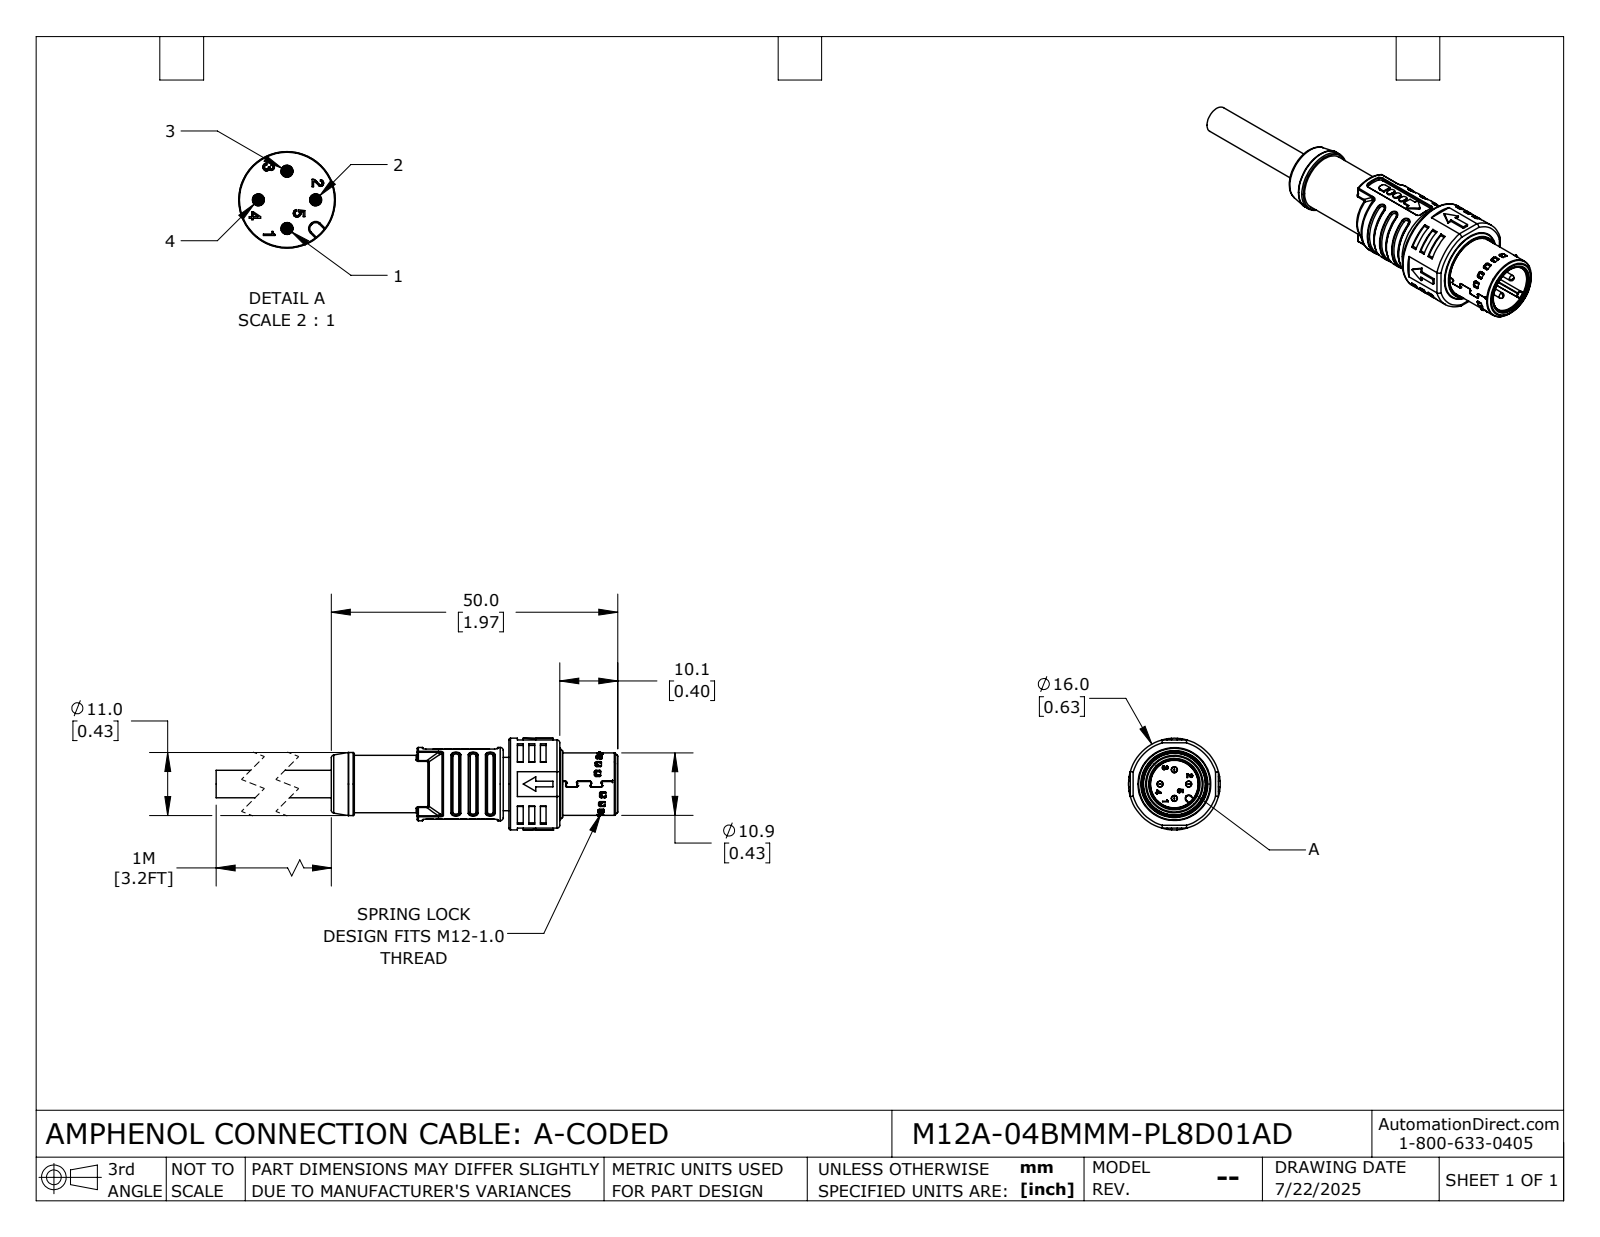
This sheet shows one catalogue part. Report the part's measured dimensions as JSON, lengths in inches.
{"part_name": "M12A-04BMMM-PL8D01AD", "step_written_by": "SolidWorks 2024 (CONFIG_CONTROL_DESIGN)", "units": "inches", "bodies": {"solids": 1, "faces": 2276, "planar": 1081, "cylindrical": 672, "other": 523}, "overall_size": [2.862, 0.63, 0.63], "volume_in3": 0.316, "surface_area_in2": 9.253, "round_holes": [[0.041, 4], [0.057, 4], [0.327, 1], [0.354, 1], [0.4, 1], [0.413, 1], [0.453, 1], [0.465, 1], [0.559, 1]], "round_bosses_or_shafts": [[0.055, 4], [0.039, 4], [0.63, 1], [0.555, 1], [0.504, 1], [0.488, 1], [0.433, 1], [0.429, 1]], "partial_cylinders_radius": [[0.008, 114], [0.01, 66], [0.012, 64], [0.006, 44], [0.02, 38], [0.005, 12], [0.028, 11], [0.004, 10]], "face_to_face_distances": [0.039, 0.398, 0.35, 0.339, 0.098, 0.059, 0.047, 1.28, 0.606, 1.618], "hole_center_spacings": [0.098, 0.139, 0.197]}
